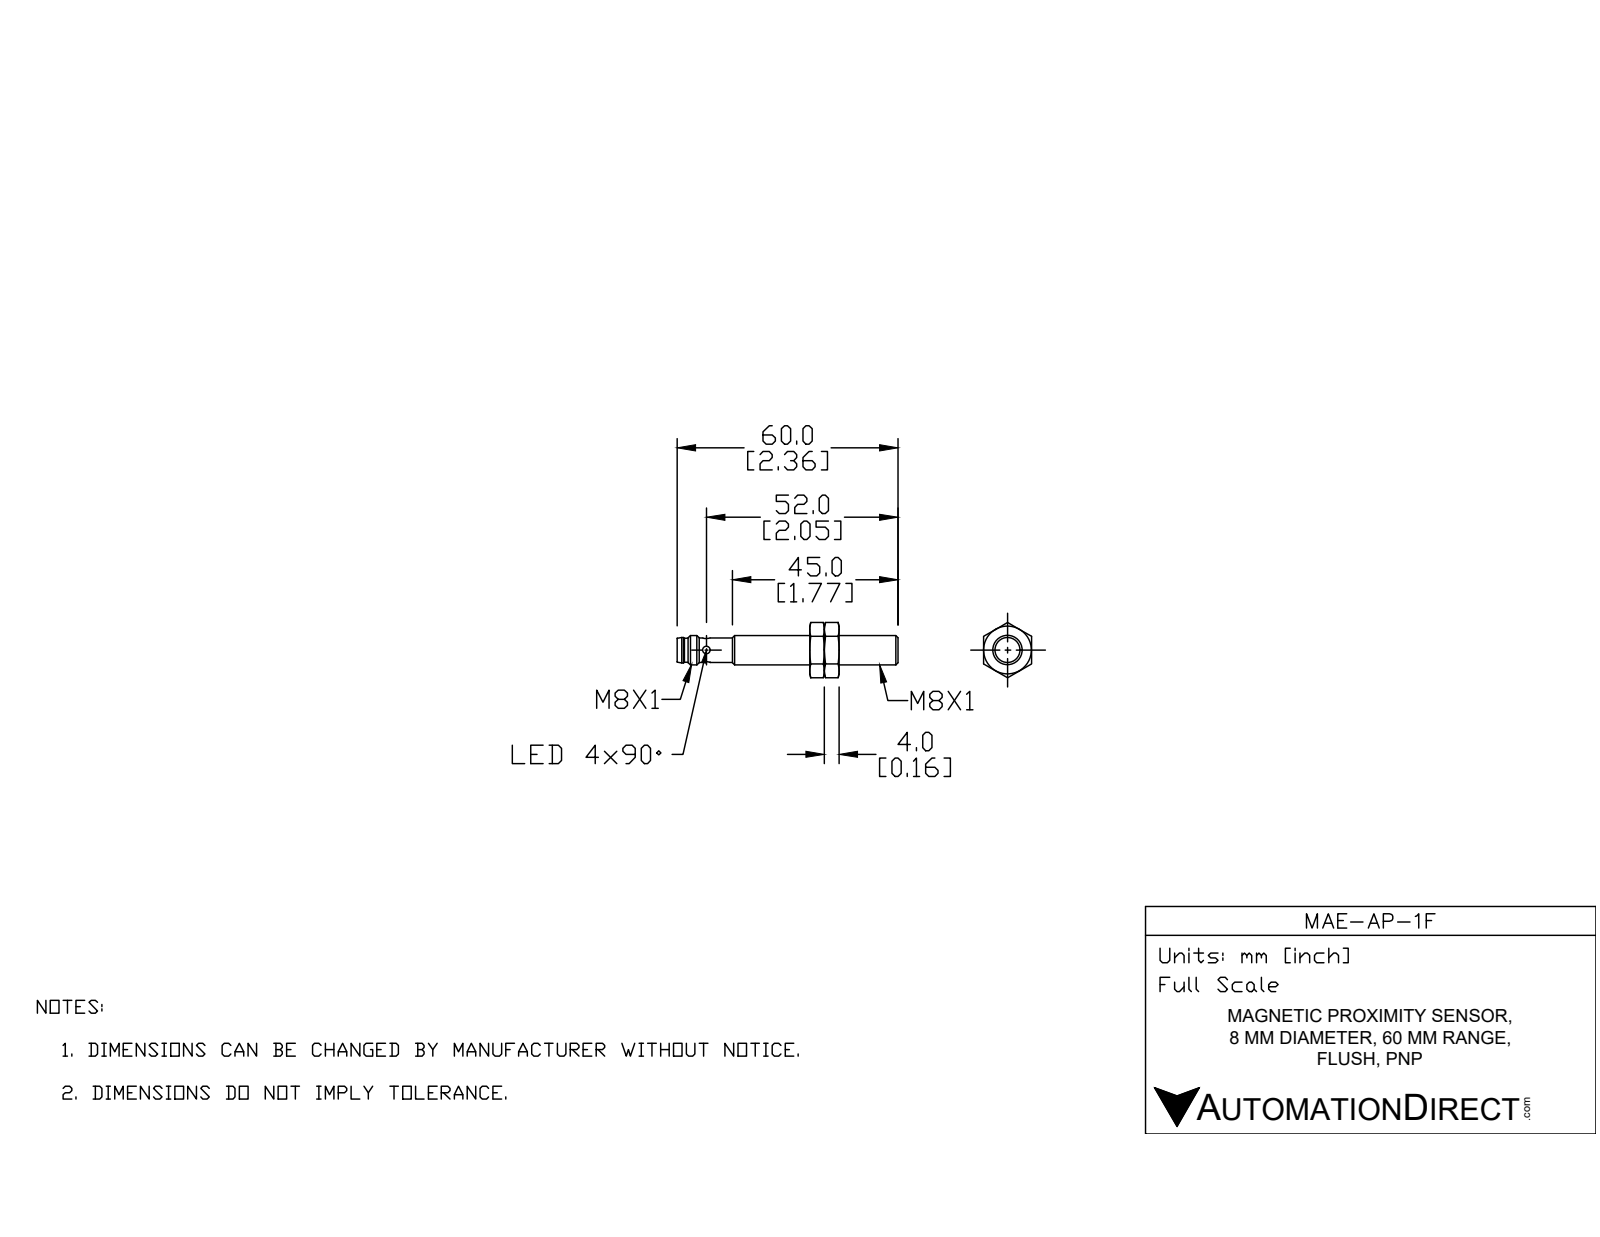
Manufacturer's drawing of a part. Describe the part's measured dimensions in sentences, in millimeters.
The part is named "MAE-AP-1F". Its 3-D file was written by "SolidWorks 2017 (AUTOMOTIVE_DESIGN)". It is 3 solids with 97 faces: 22 planar, 29 cylindrical and 46 other. Overall it measures 60 by 15 by 13 millimeters. Its volume is 3 490 cubic millimeters and its surface area 2 601 square millimeters. Round holes: 2 of diameter 2, 1 of diameter 5.8, 1 of diameter 6.9. Round bosses or shafts: 1 of diameter 8, 1 of diameter 6.9, 1 of diameter 6.6, 1 of diameter 6.5. Partial cylindrical surfaces (rounded edges, fillets, slot ends): 1 of radius 3. The main face-to-face distances are 13, 4, 8, 24, 20, 16, 29.8, 33.8, 37.8, 53.8.
